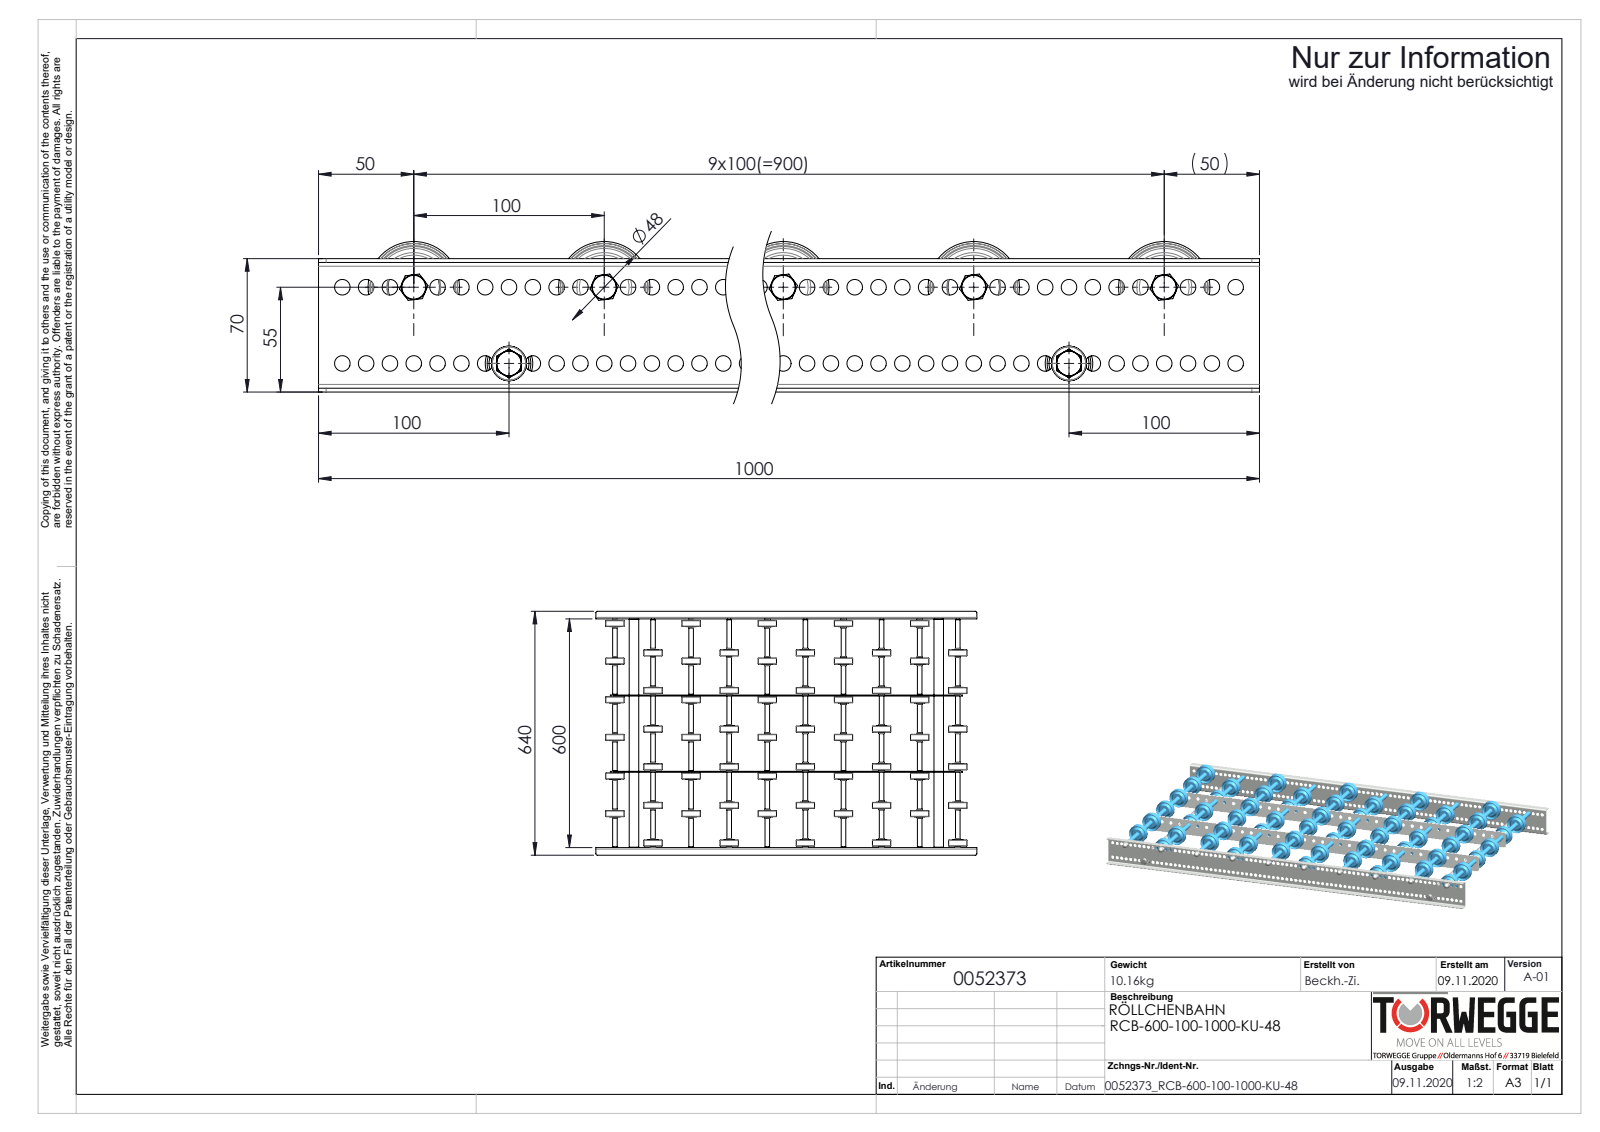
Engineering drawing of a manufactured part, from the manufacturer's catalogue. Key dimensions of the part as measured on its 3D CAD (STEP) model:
Part name (STEP PRODUCT): 0011532_2300-48-8; S100100_Längstraverse-42x2,5_S100101_Lngstraverse-RB-L975; Hutmutter_DIN_1587_M8; 0052373 (+6 more)
STEP written by: SolidWorks 2020 (AUTOMOTIVE_DESIGN)
Units: millimetres
Bodies: 164 solids, 6220 faces (1092 planar, 2264 cylindrical, 2864 other)
Overall size (bounding box): 1000 × 640 × 79
Volume: 2 416 000 mm³ · Surface area: 1 813 000 mm²
Round holes (diameter × count): ⌀8.2 ×158, ⌀8.5 ×37, ⌀6.65 ×10, ⌀9.65 ×10, ⌀13.7 ×10, ⌀6.8 ×2, ⌀21 ×2
Round bosses / shafts (diameter × count): ⌀8 ×12, ⌀48 ×10, ⌀27 ×10, ⌀12.7 ×10, ⌀12.5 ×10, ⌀12 ×10, ⌀25 ×2
Partial cylindrical surfaces — rounded edges, fillets, slot ends (radius × count): R4 ×8, R2 ×4, R5 ×4
Main face-to-face distances: 2, 200.1, 602, 2.5, 197.6, 68, 604, 600, 400.2, 201.8
Hole centre spacings: 12.5, 25, 37.5, 50, 62.5, 75, 87.5, 100
